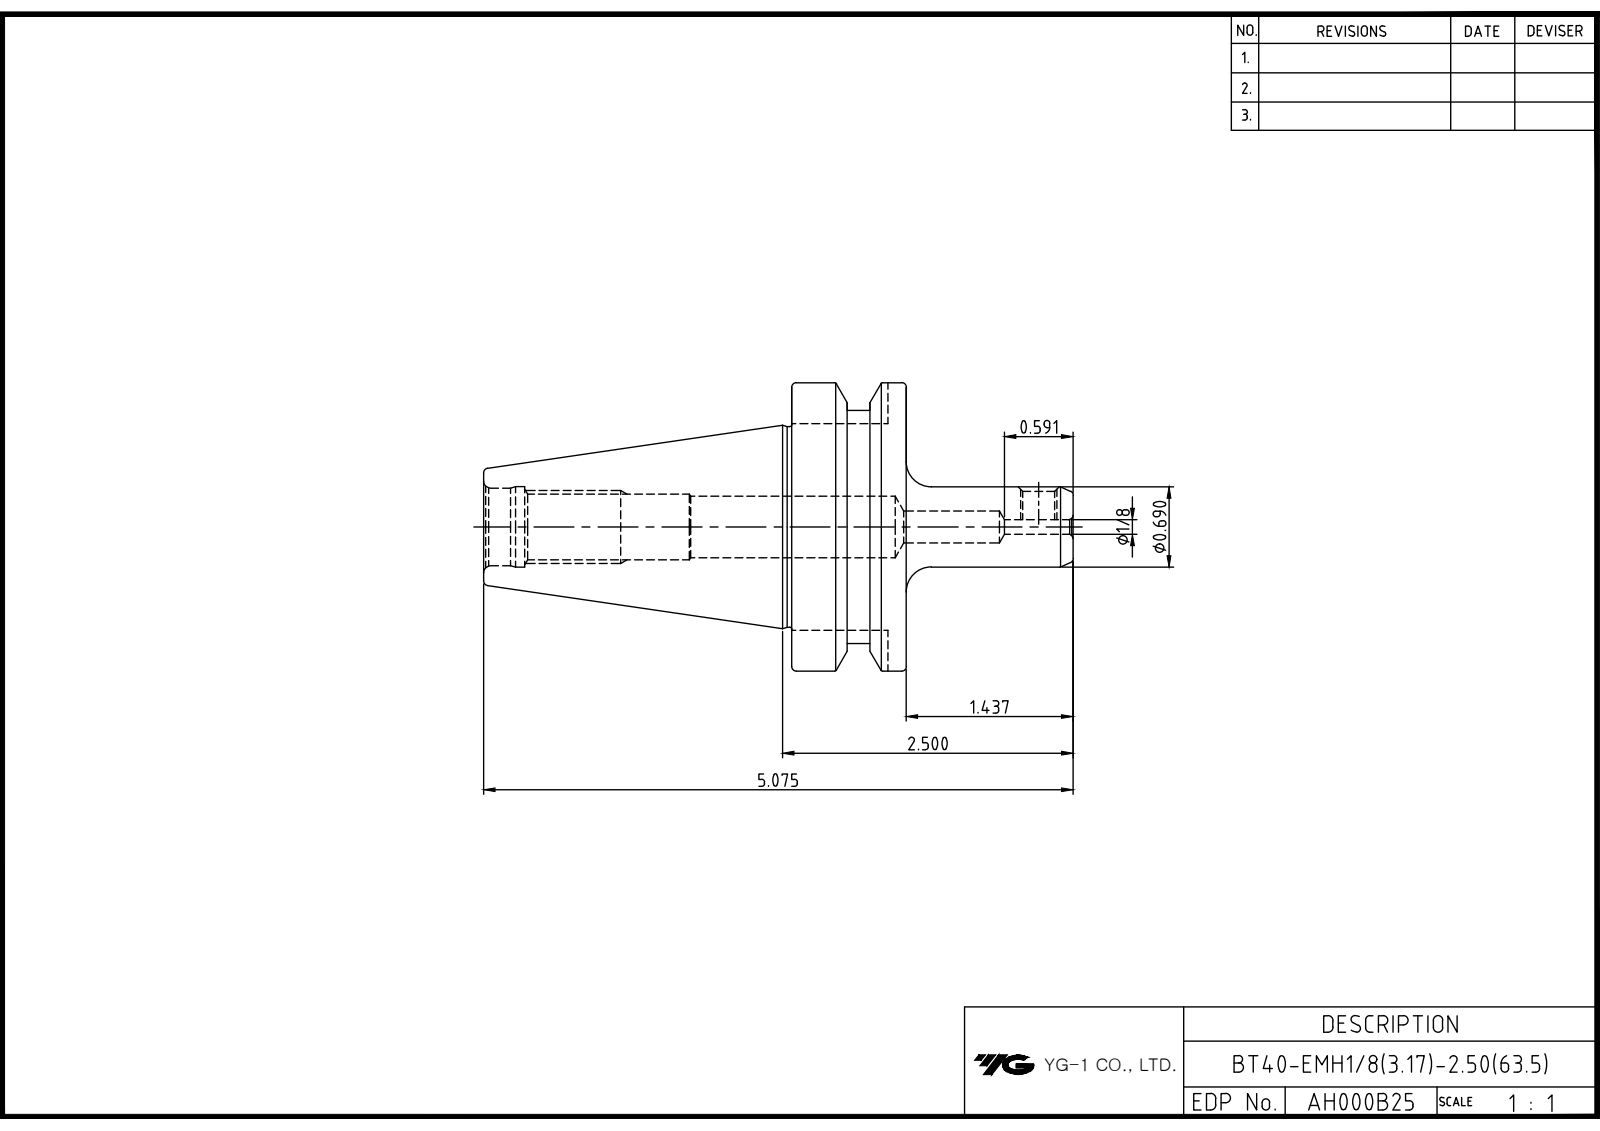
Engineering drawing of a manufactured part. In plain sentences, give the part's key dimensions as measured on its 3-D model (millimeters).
The part is named "LO-BT40-EMH3.175-63.5". Its 3-D file was written by "Autodesk Inventor 2022 (AUTOMOTIVE_DESIGN)". It is 1 solid with 53 faces: 15 planar, 16 cylindrical and 22 other. Overall it measures 128.9 by 63 by 63 millimeters. Its volume is 130 703 cubic millimeters and its surface area 24 716 square millimeters. Round holes: 1 of diameter 3.17, 1 of diameter 3.3, 1 of diameter 7, 1 of diameter 13.5, 1 of diameter 13.84, 1 of diameter 17, 1 of diameter 17.6. Round bosses or shafts: 1 of diameter 63, 1 of diameter 52.6, 1 of diameter 44, 1 of diameter 17.53. Partial cylindrical surfaces (rounded edges, fillets, slot ends): 1 of radius 8.05. The main face-to-face distances are 25, 45.2, 16.1, 67.4, 92.4, 128.9, 61.5, 36.5, 84.5, 17.1.
